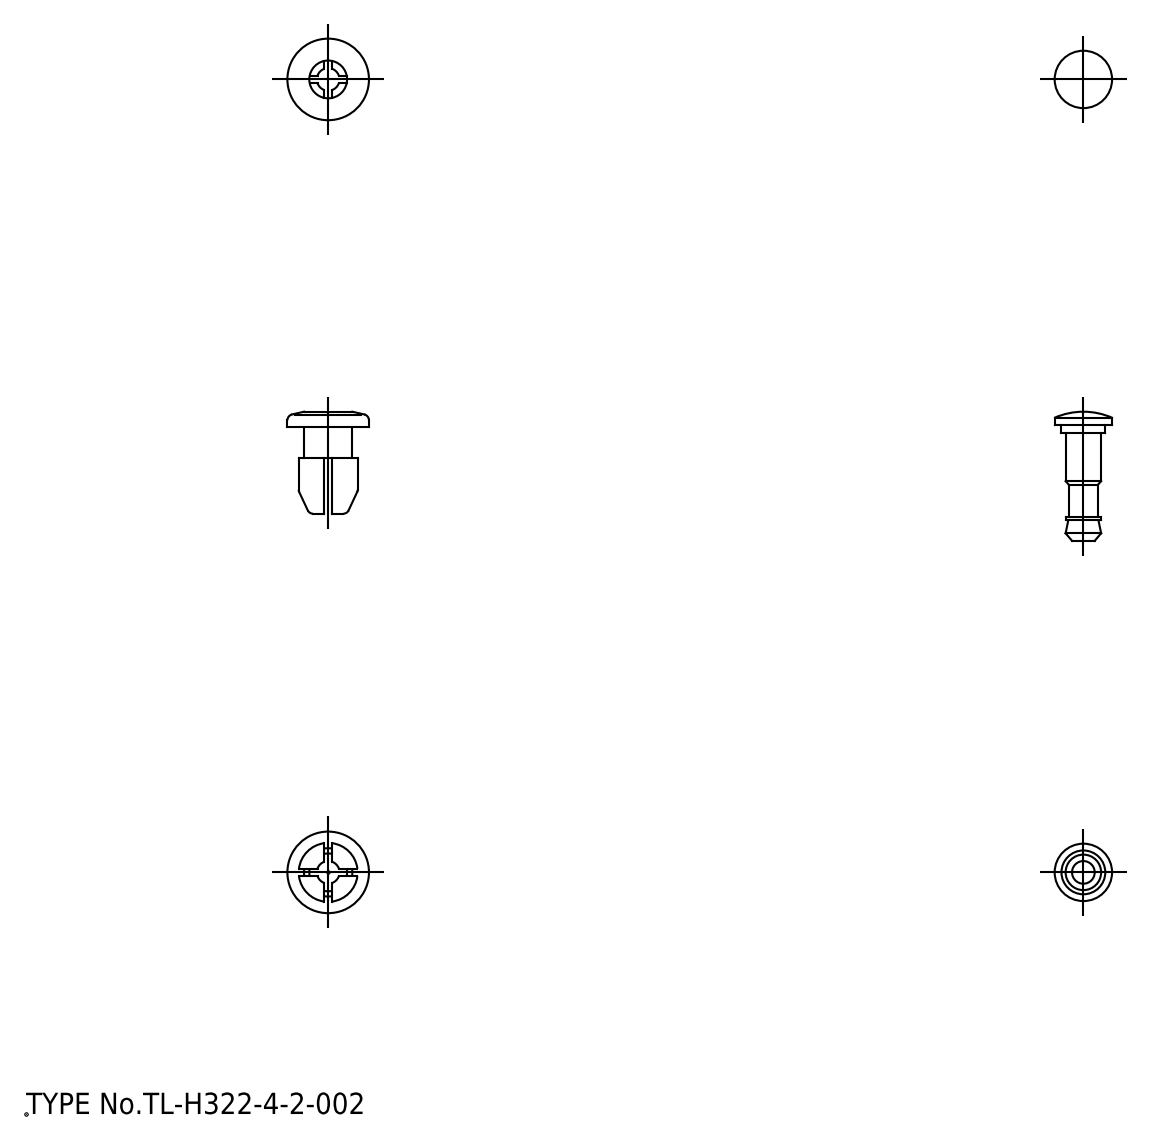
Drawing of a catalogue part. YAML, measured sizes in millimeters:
part_name: "grommet; plunger"
step_written_by: "spGate 18.9.1 (****-****-****-****) (AUTOMOTIVE_DESIGN)"
units: millimeters
bodies: {solids: 2, faces: 79, planar: 27, cylindrical: 24, other: 28}
overall_size: [19.1, 10.8, 10.8]
volume: 630
surface_area: 1019
round_holes:
  - {diameter: 5, count: 1}
round_bosses_or_shafts:
  - {diameter: 10.8, count: 1}
  - {diameter: 7.8, count: 1}
  - {diameter: 7.6, count: 1}
  - {diameter: 6.4, count: 1}
  - {diameter: 5.8, count: 1}
  - {diameter: 4.7, count: 1}
  - {diameter: 3.8, count: 1}
partial_cylinders:
  - {radius: 1.5, count: 1}
face_to_face_distances: [1, 5.8, 2, 4.1, 9.9, 6.1, 3.8, 11.5, 2.7, 8.9]
